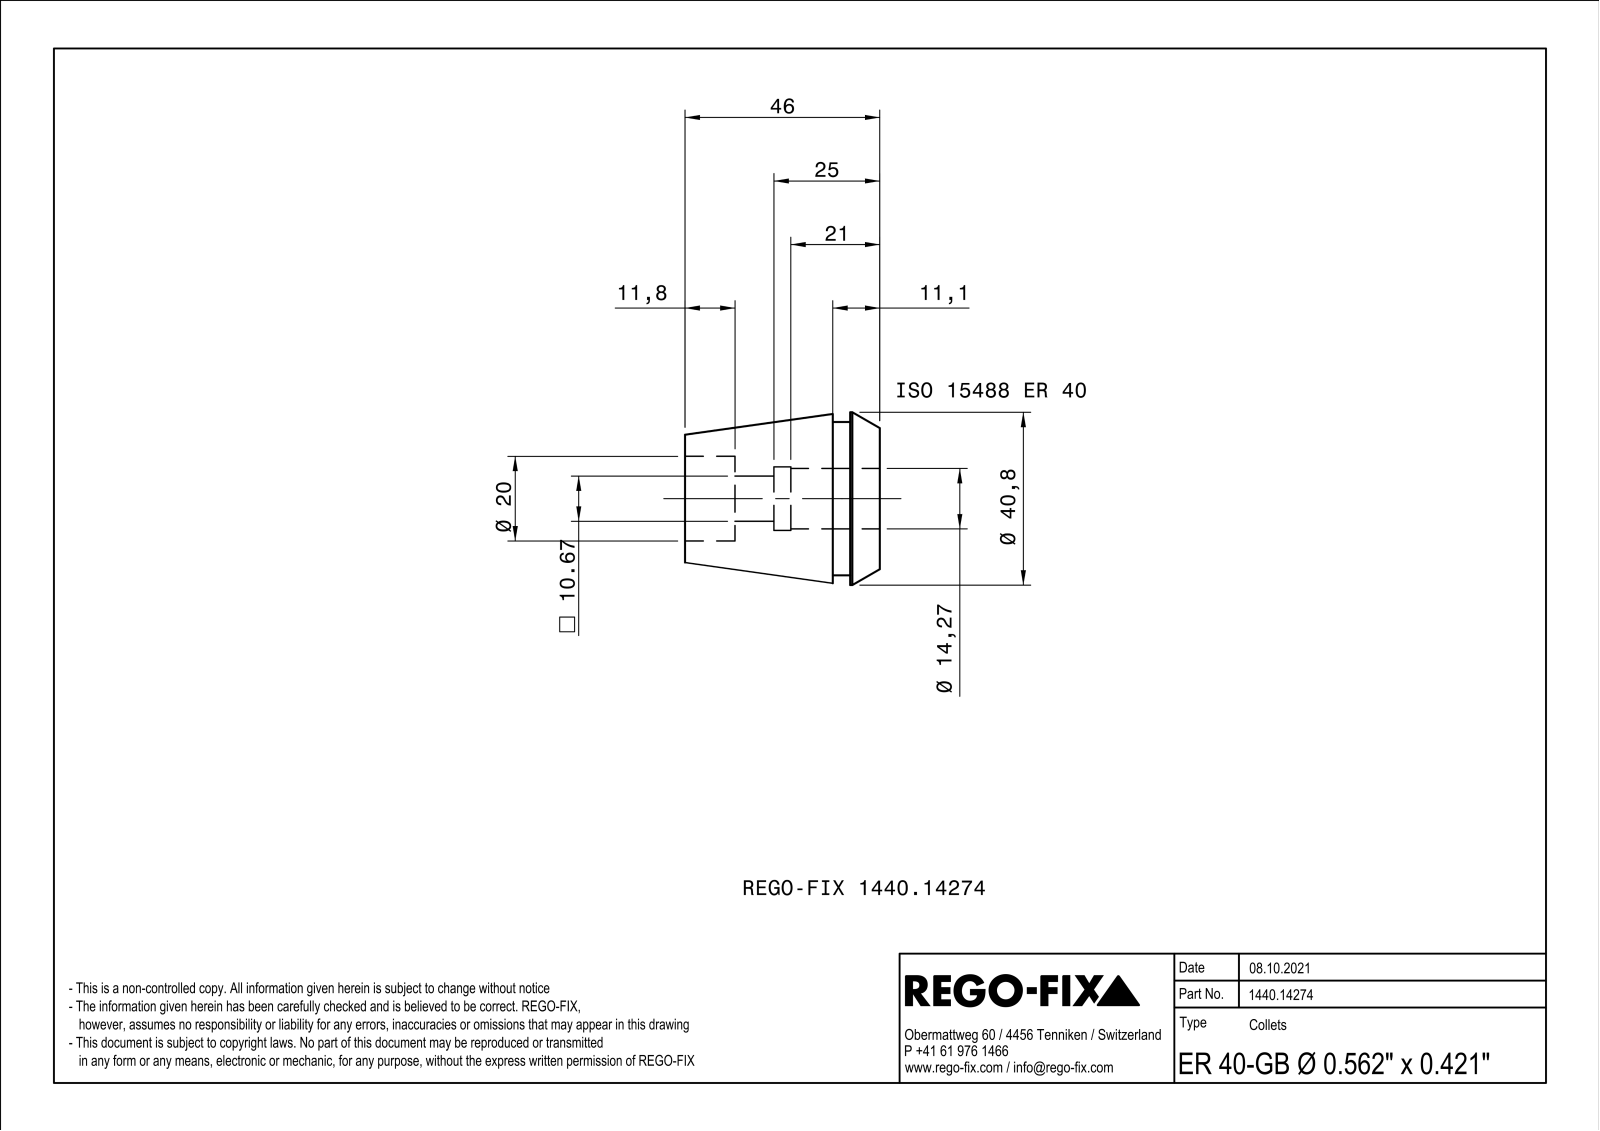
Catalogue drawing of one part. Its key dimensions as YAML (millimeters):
part_name: "NOCUT"
step_written_by: "SIEMENS PLM Software Solid Edge ST10 (AUTOMOTIVE_DESIGN)"
units: millimeters
bodies: {solids: 1, faces: 168, planar: 68, cylindrical: 36, other: 64}
overall_size: [46, 40.79, 40.79]
volume: 33589
surface_area: 15063
round_holes:
  - {diameter: 14.27, count: 1}
  - {diameter: 15, count: 1}
  - {diameter: 20, count: 1}
round_bosses_or_shafts:
  - {diameter: 36.2, count: 1}
partial_cylinders:
  - {radius: 6.3, count: 1}
  - {radius: 7.4, count: 1}
face_to_face_distances: [1, 46, 7, 39, 11.1, 4.1, 34.9, 5.1, 6.1, 34.2]
